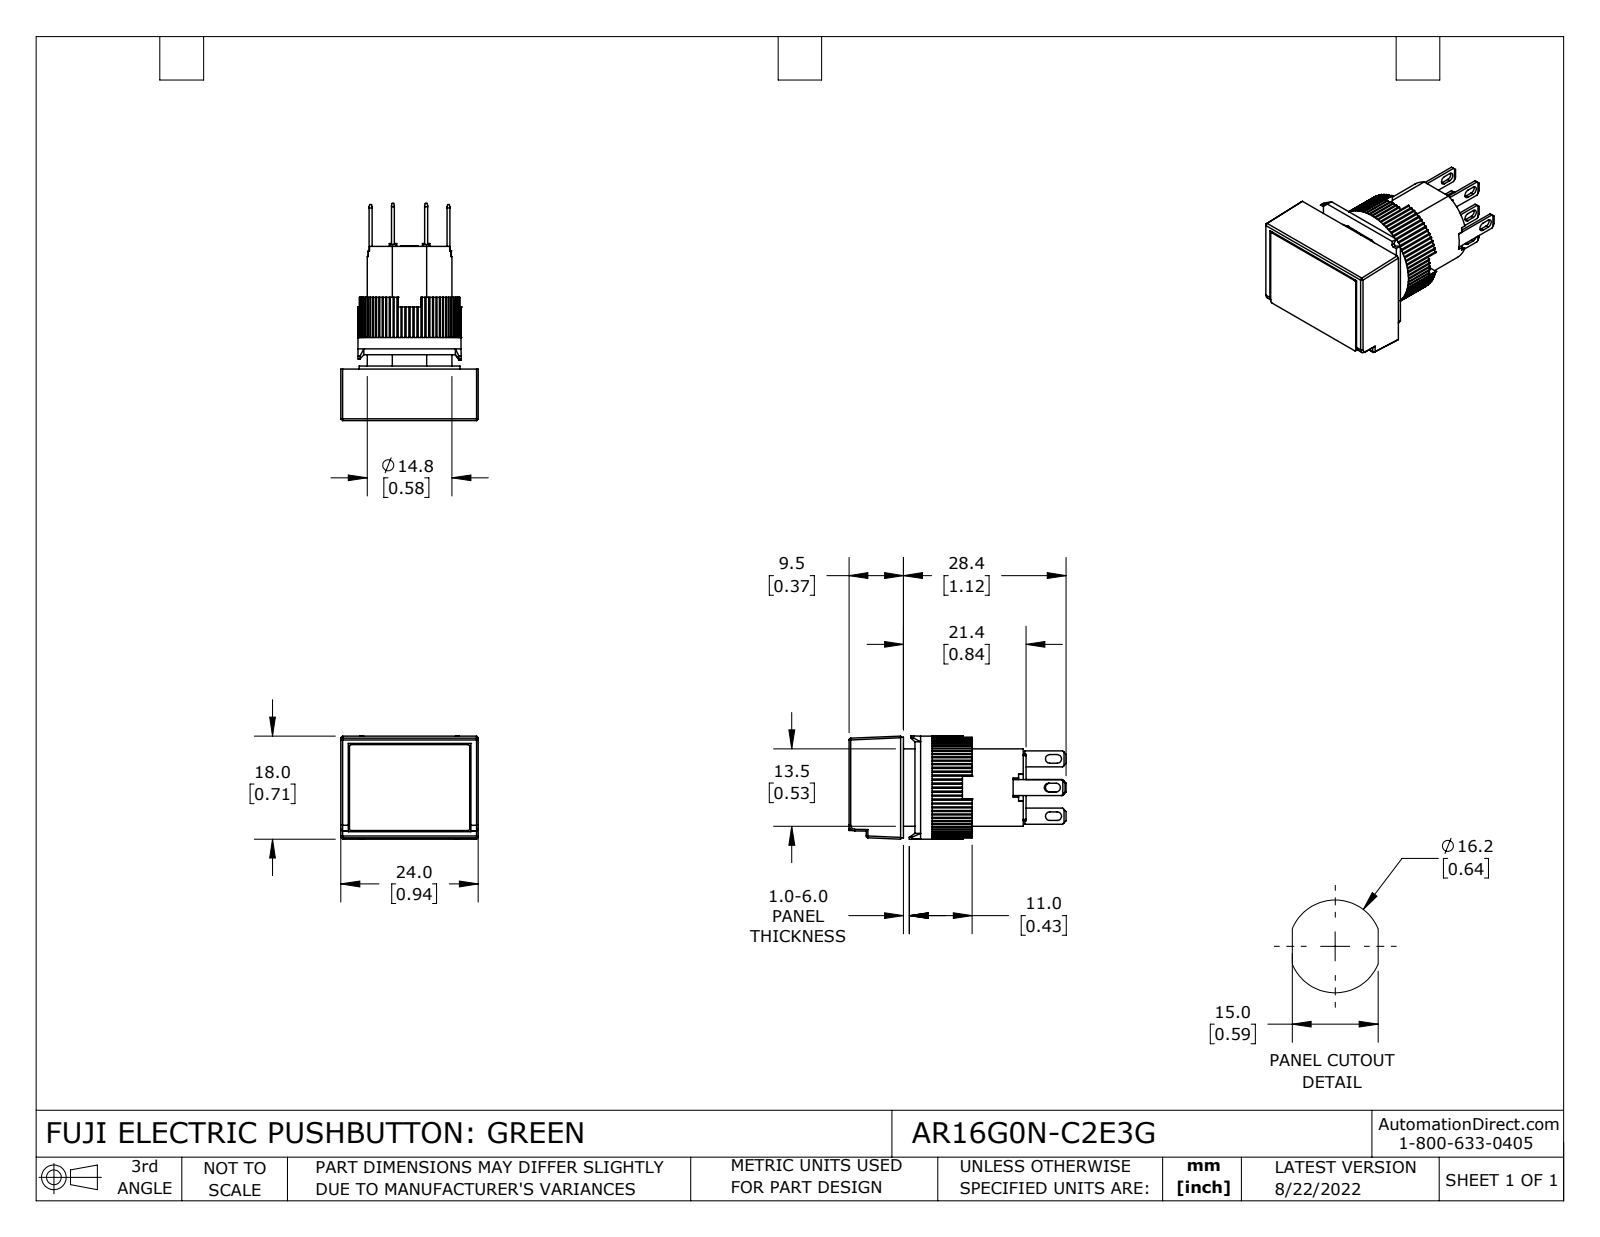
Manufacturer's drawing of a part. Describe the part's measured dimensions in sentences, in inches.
The part is named "AR16G0N-C2E3G". Its 3-D file was written by "SolidWorks 2021 (CONFIG_CONTROL_DESIGN)". It is 14 solids with 841 faces: 654 planar, 181 cylindrical and 6 other. Overall it measures 1.492 by 0.945 by 0.709 inches. Its volume is 0.448 cubic inches and its surface area 9.503 square inches. Round holes: 1 of diameter 0.543, 1 of diameter 0.583. Round bosses or shafts: 1 of diameter 0.709, 1 of diameter 0.693. Partial cylindrical surfaces (rounded edges, fillets, slot ends): 80 of radius 0.01, 12 of radius 0.008, 8 of radius 0.03, 6 of radius 0.012, 1 of radius 0.039. The main face-to-face distances are 0.213, 0.354, 0.142, 0.35, 0.492, 0.138, 0.02, 0.843, 0.059, 0.453.
